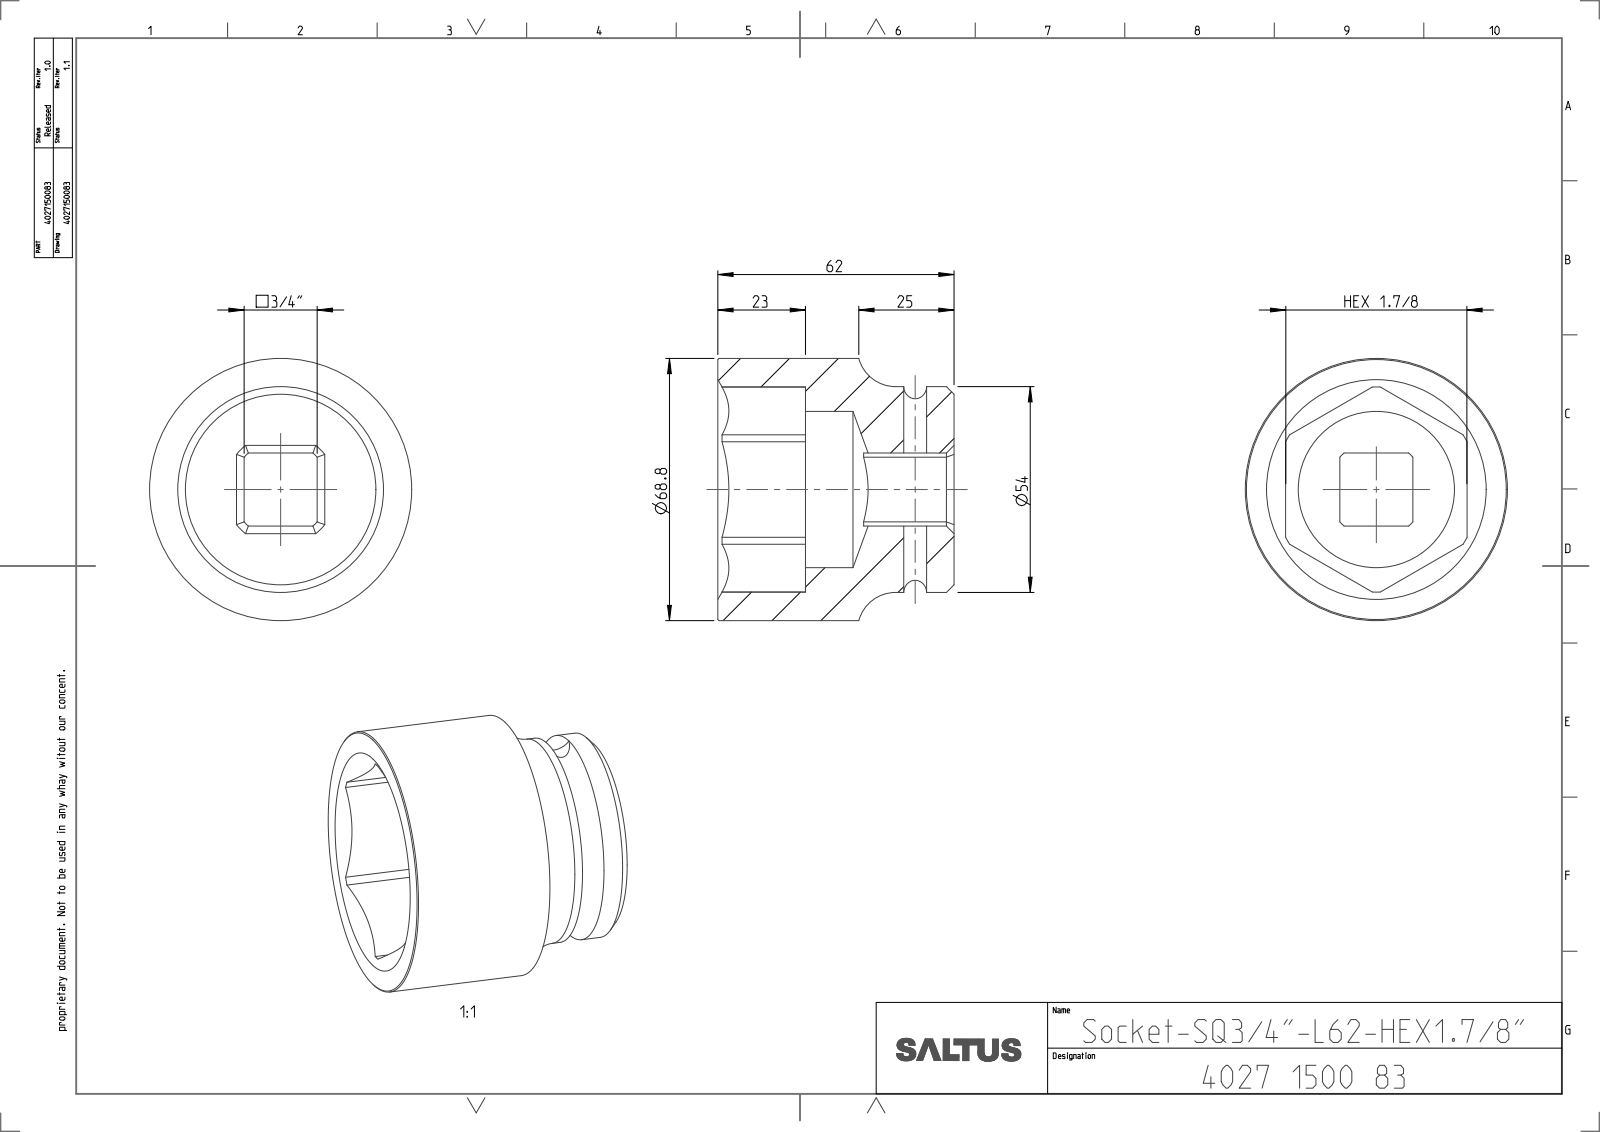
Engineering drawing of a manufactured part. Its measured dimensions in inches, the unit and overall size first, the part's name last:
Units: inches
Overall size (bounding box): 2.709 × 2.709 × 2.441
Round holes (diameter × count): ⌀0.236 ×1, ⌀1.614 ×1
Round bosses / shafts (diameter × count): ⌀2.709 ×1, ⌀2.126 ×1
Partial cylindrical surfaces — rounded edges, fillets, slot ends (radius × count): R0.504 ×1, R1.059 ×1
Main face-to-face distances: 2.441, 1.875, 0.56, 1.315, 0.755, 1.535, 0.906, 1.876
Volume: 7.386 in³ · Surface area: 39.95 in²
Bodies: 1 solid, 55 faces (17 planar, 22 cylindrical, 16 other)
Part name (STEP PRODUCT): 4027150083
STEP written by: CREO PARAMETRIC BY PTC INC, 2022414 (CONFIG_CONTROL_DESIGN)
